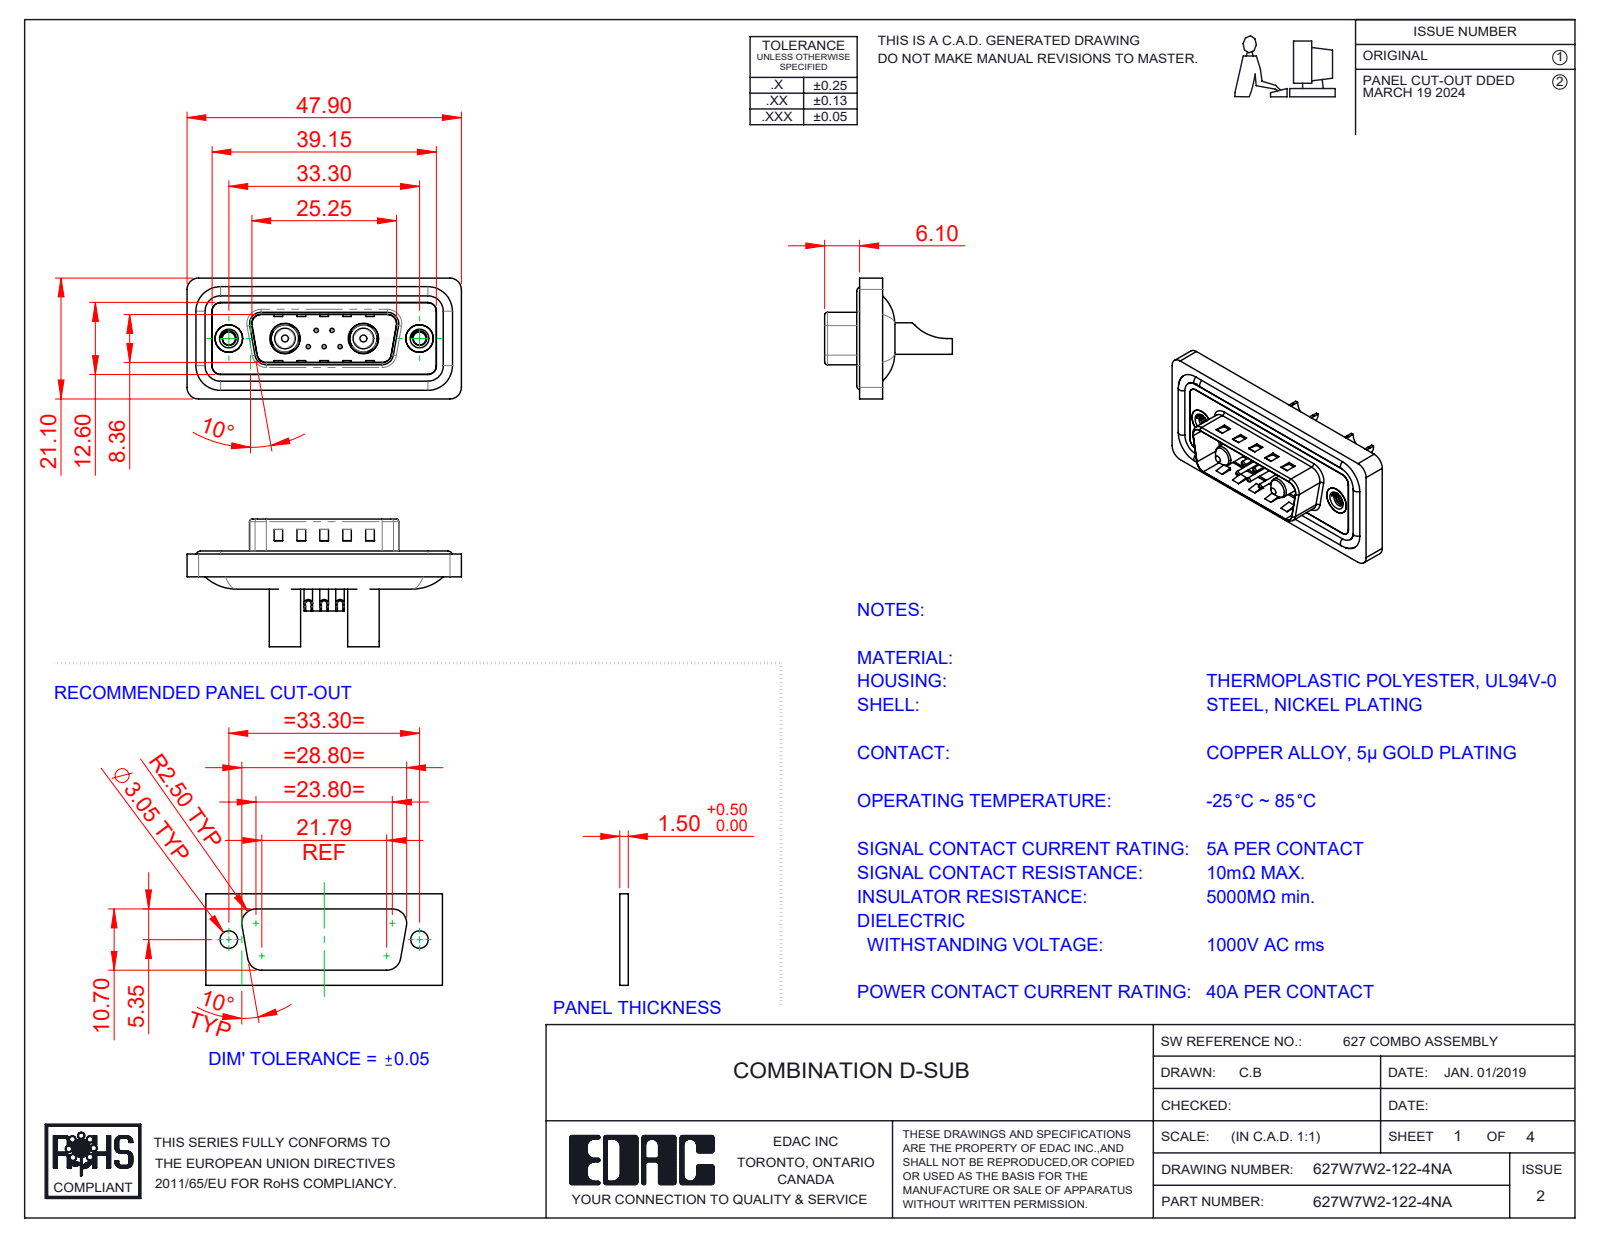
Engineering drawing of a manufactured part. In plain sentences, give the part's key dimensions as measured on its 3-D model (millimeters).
The part is named "627Combo Housing_7W2; 627W7W2-122-4NA; Power Pin_40A SC; 627Combo Contact Row 2_22 (+5 more)". Its 3-D file was written by "SolidWorks 2023 (CONFIG_CONTROL_DESIGN)". It is 16 solids with 714 faces: 246 planar, 306 cylindrical and 162 other. Overall it measures 47.9 by 22.3 by 21.1 millimeters. Its volume is 5 606 cubic millimeters and its surface area 9 110 square millimeters. Round holes: 5 of diameter 0.75, 5 of diameter 1, 5 of diameter 1.6, 5 of diameter 2, 2 of diameter 2.26, 2 of diameter 4, 2 of diameter 4.6, 2 of diameter 4.8, 2 of diameter 4.85, 2 of diameter 5, 2 of diameter 5.3. Round bosses or shafts: 5 of diameter 1.5, 4 of diameter 1.6, 2 of diameter 5.5, 2 of diameter 5.2, 2 of diameter 4.9, 2 of diameter 4.75, 2 of diameter 3.75, 2 of diameter 3.6. Partial cylindrical surfaces (rounded edges, fillets, slot ends): 26 of radius 1.5, 20 of radius 2, 8 of radius 0.5, 8 of radius 1.6, 6 of radius 1, 4 of radius 0.25, 4 of radius 0.6, 4 of radius 0.65. The main face-to-face distances are 0.4, 1.1, 1.6, 0.5, 1.5, 3.1, 2.9, 0.82, 9.58, 2.5. The hole center spacings are 3.16, 2.77, 9.8, 23.5, 4.31, 4.33, 5.03, 5.04.
